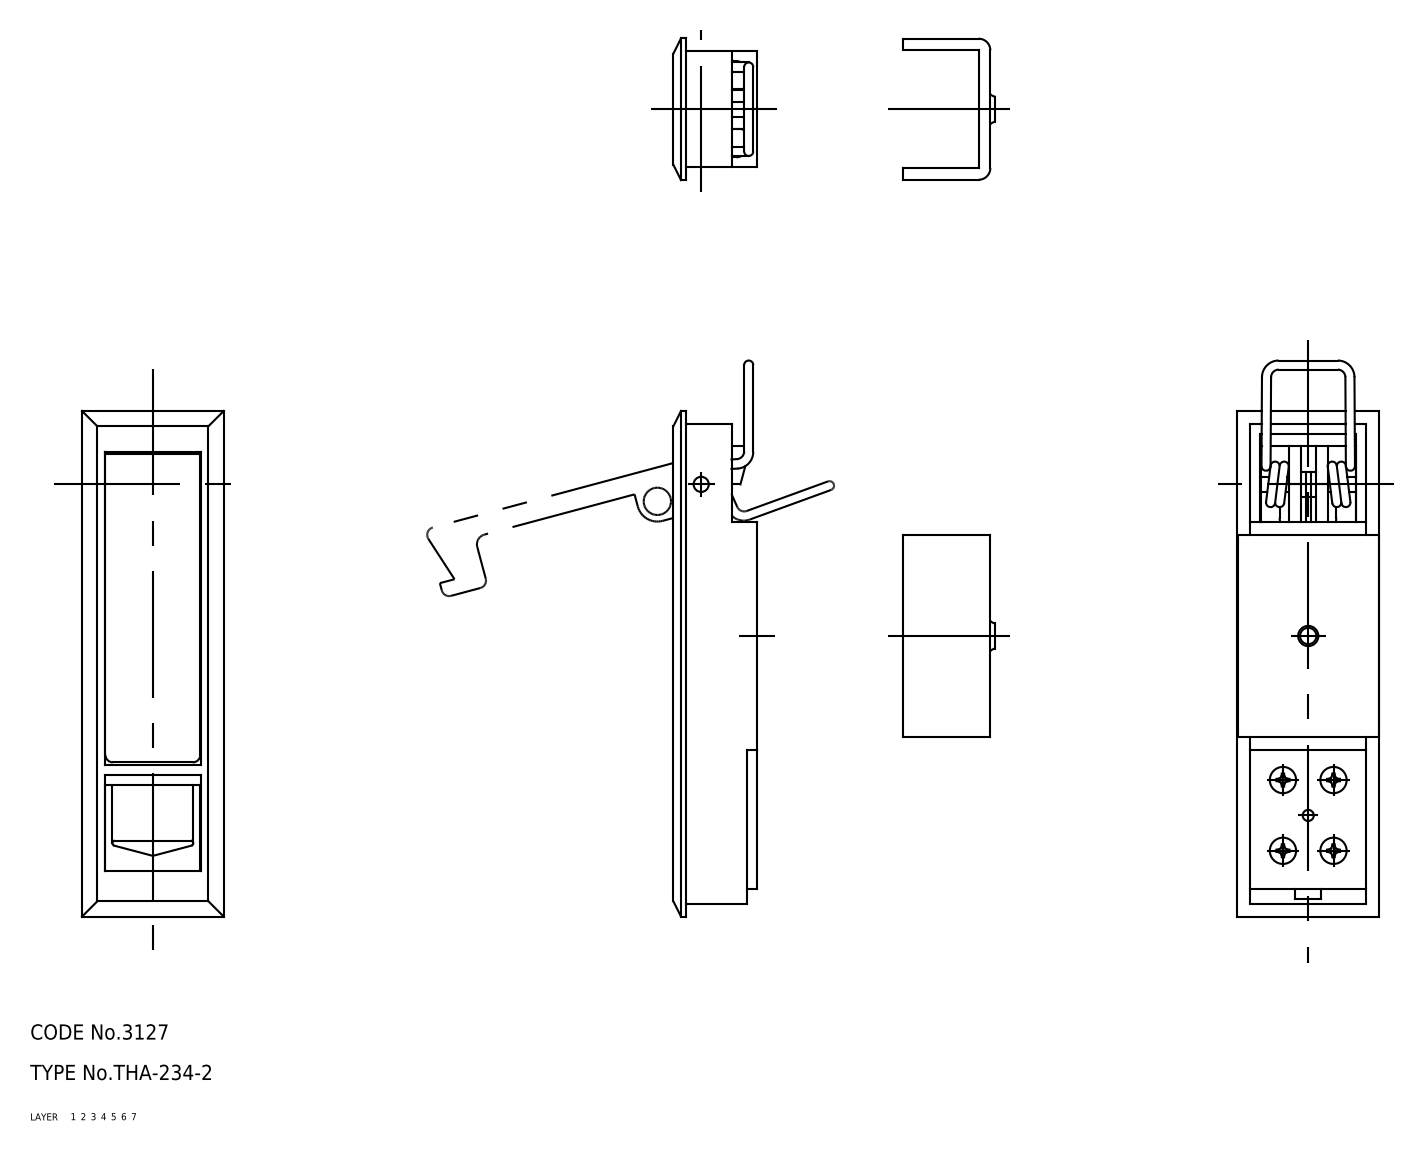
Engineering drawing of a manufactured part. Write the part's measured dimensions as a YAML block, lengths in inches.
part_name: "cam; handle; latch; housing (+2 more)"
step_written_by: "CADfix (AUTOMOTIVE_DESIGN)"
units: inches
bodies: {solids: 5, faces: 339, planar: 0, cylindrical: 0, other: 339}
overall_size: [4.331, 1.102, 0.819]
volume: 1.639
surface_area: 38.35
